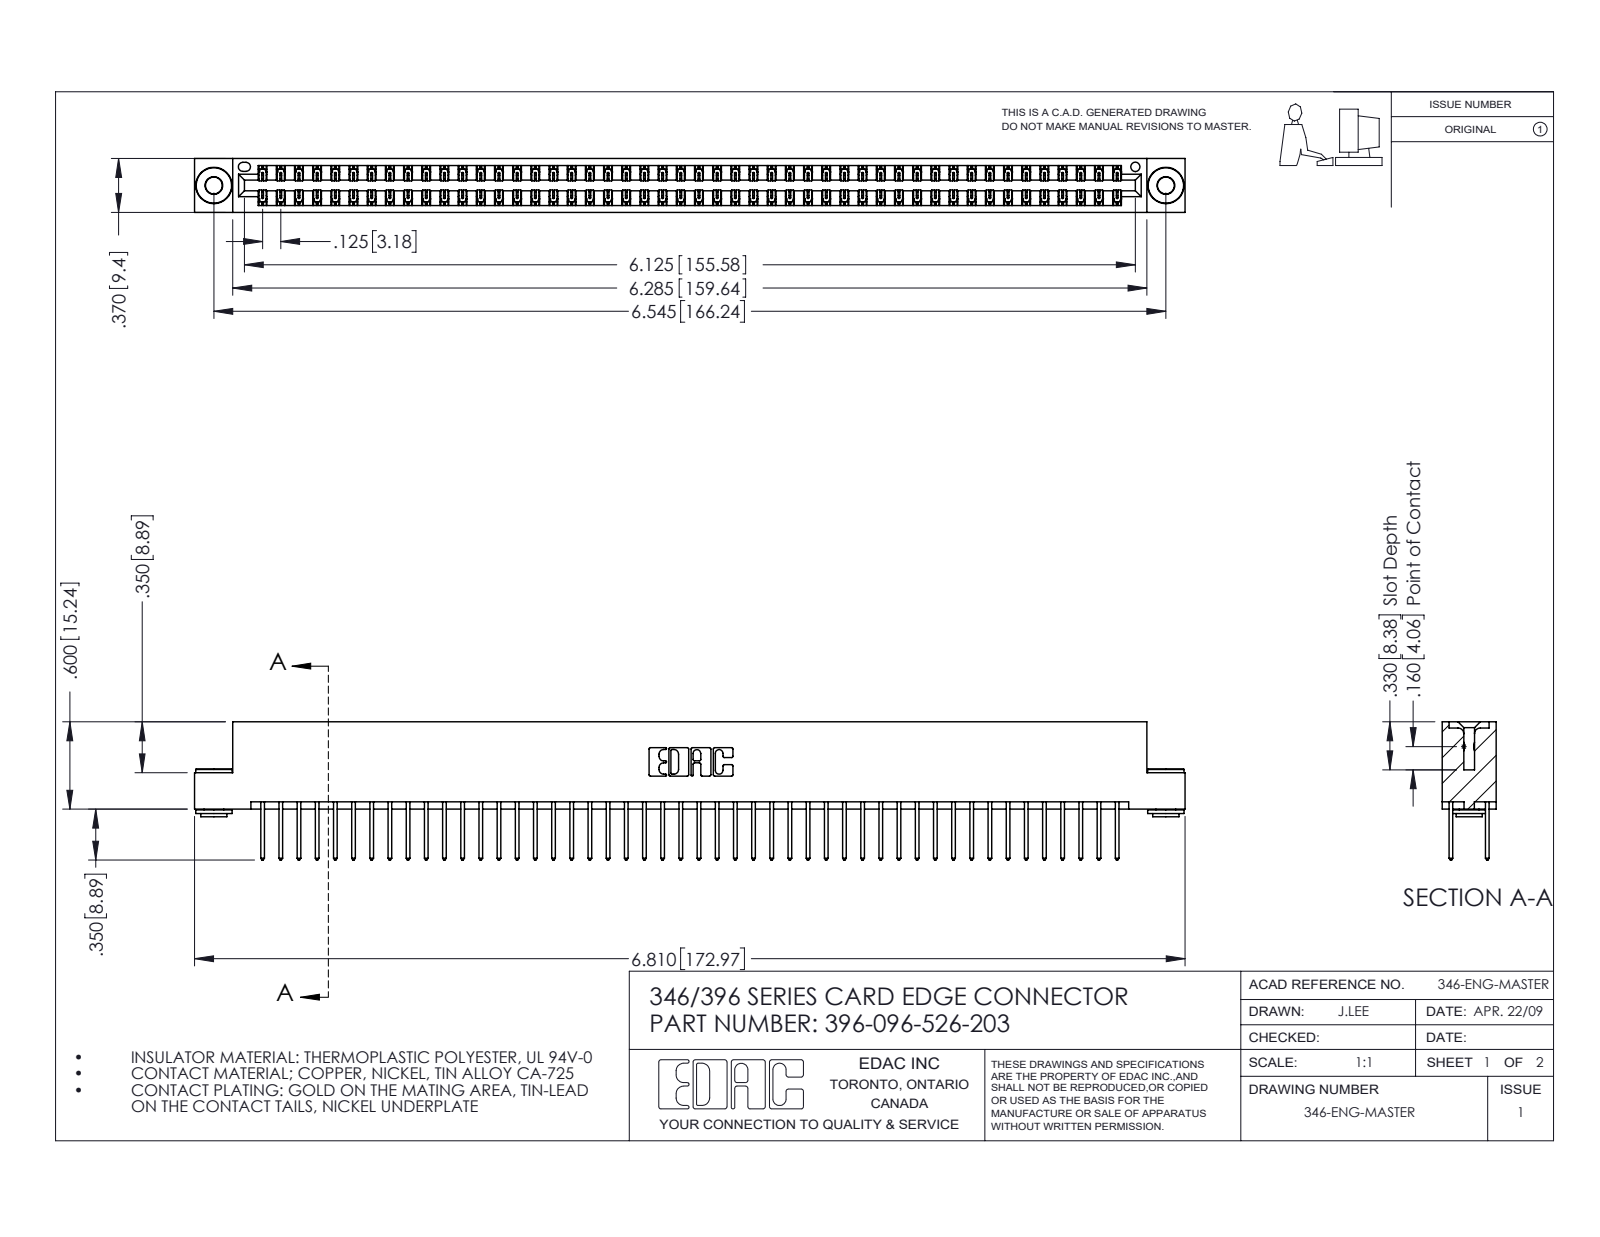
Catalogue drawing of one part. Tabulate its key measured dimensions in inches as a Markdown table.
| quantity | value |
| --- | --- |
| part name | 396-096-526-203; 346 Part_Flush Mounting Lugs - 0.156 Dia-TH; 345-250-002_345-250-002-102; 345-292-001_345-293-126 |
| STEP written by | SolidWorks 2016 (CONFIG_CONTROL_DESIGN) |
| units | inches |
| bodies | 99 solids, 5152 faces (3446 planar, 1698 cylindrical, 8 other) |
| overall size | 6.81 × 0.95 × 0.37 |
| volume | 1.043 in³ |
| surface area | 37.98 in² |
| round holes (diameter × count) | 0.116 × 2, 0.156 × 2, 0.064 × 1 |
| round bosses / shafts (diameter × count) | 0.25 × 2, 0.18 × 2, 0.136 × 2 |
| partial cylindrical surfaces (radius × count) | 0.006 × 144, 0.01 × 96, 0.01 × 22, 0.007 × 6, 0.031 × 6, 0.026 × 3, 0.014 × 2, 0.022 × 2 |
| main face-to-face distances | 0.048, 0.322, 0.25, 0.37, 0.025, 0.072, 0.298, 0.275, 0.148, 0.222 |
| hole center spacings | 0.246, 6.336, 6.545 |
